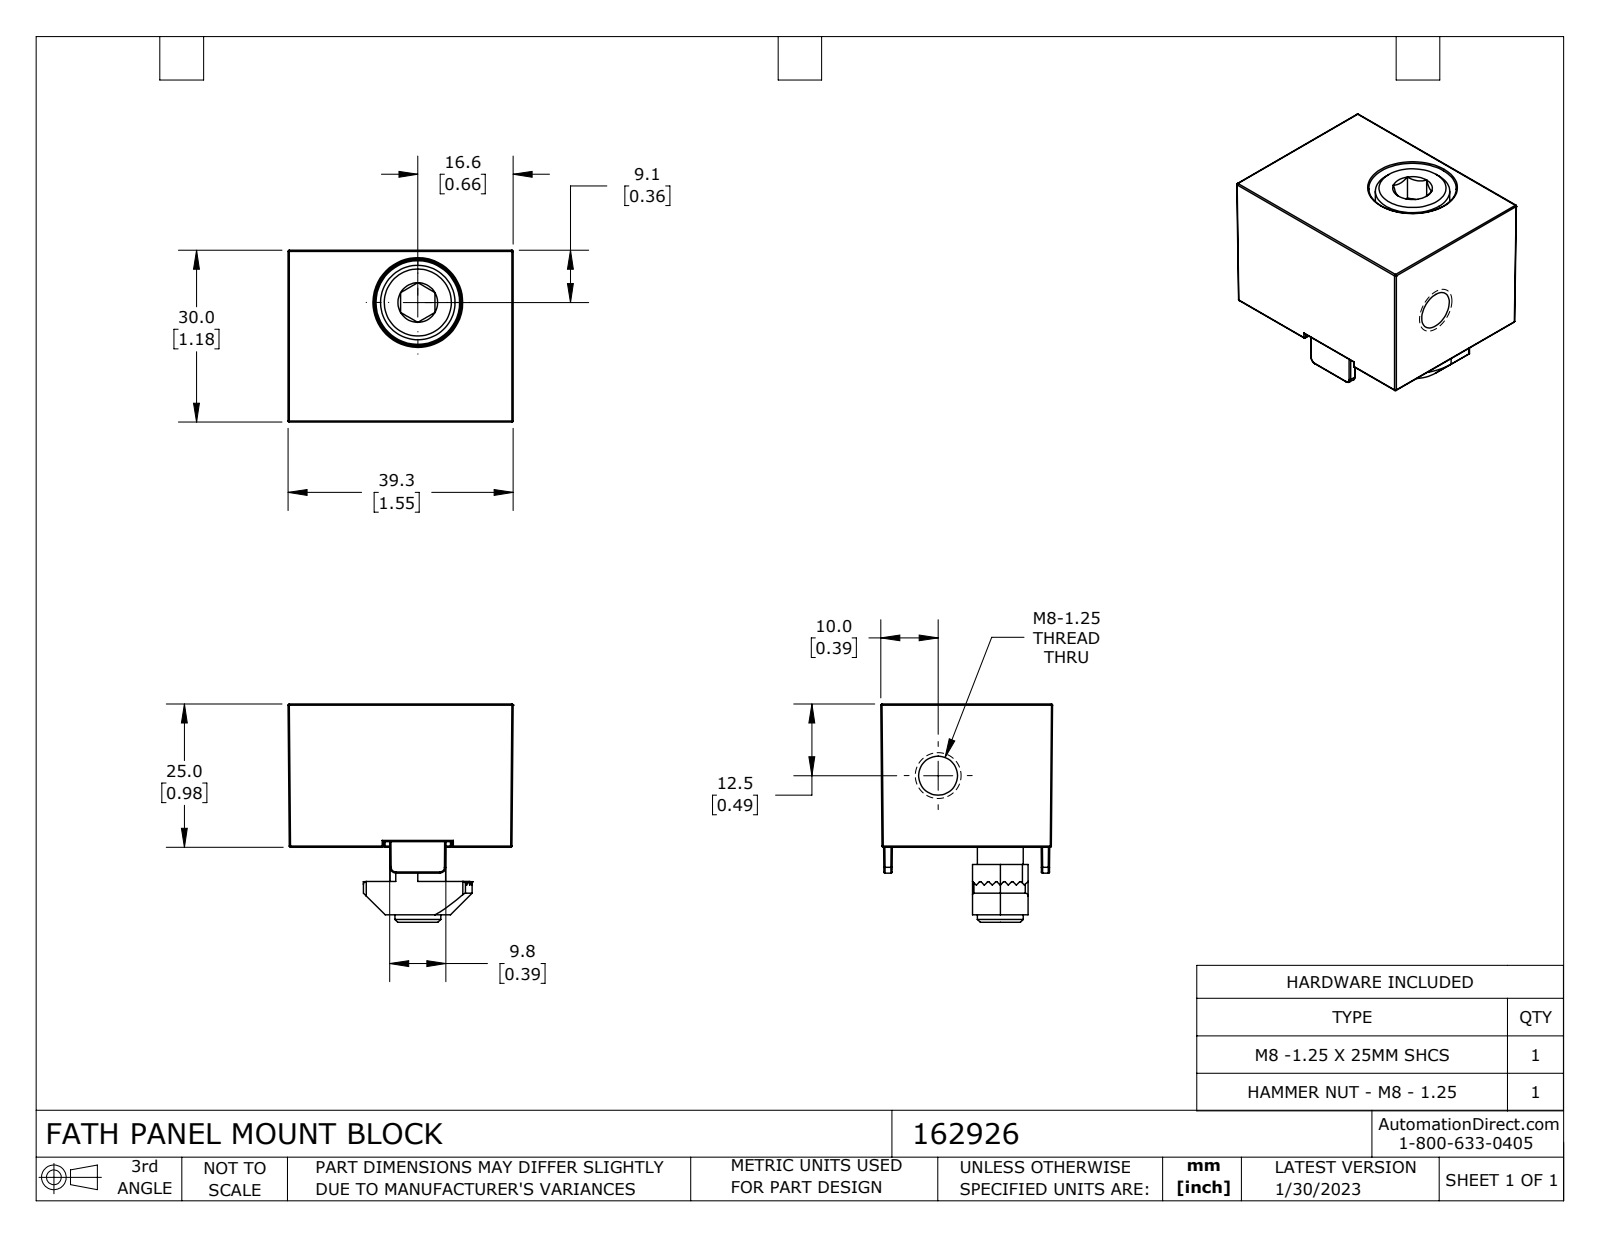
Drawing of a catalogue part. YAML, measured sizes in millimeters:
part_name: "162926"
step_written_by: "SolidWorks 2021 (CONFIG_CONTROL_DESIGN)"
units: millimeters
bodies: {solids: 2, faces: 341, planar: 96, cylindrical: 129, other: 116}
overall_size: [39.3, 38.1, 30]
volume: 20960
surface_area: 11630
round_holes:
  - {diameter: 6.8, count: 2}
round_bosses_or_shafts:
  - {diameter: 13, count: 1}
  - {diameter: 8, count: 1}
partial_cylinders:
  - {radius: 0.2, count: 75}
  - {radius: 0.5, count: 10}
  - {radius: 1, count: 4}
  - {radius: 4.9, count: 1}
  - {radius: 5.4, count: 1}
  - {radius: 9.5, count: 1}
face_to_face_distances: [25, 10.1, 26.5, 20.5, 14.9, 3, 12.8, 9.7, 27.5, 1]
